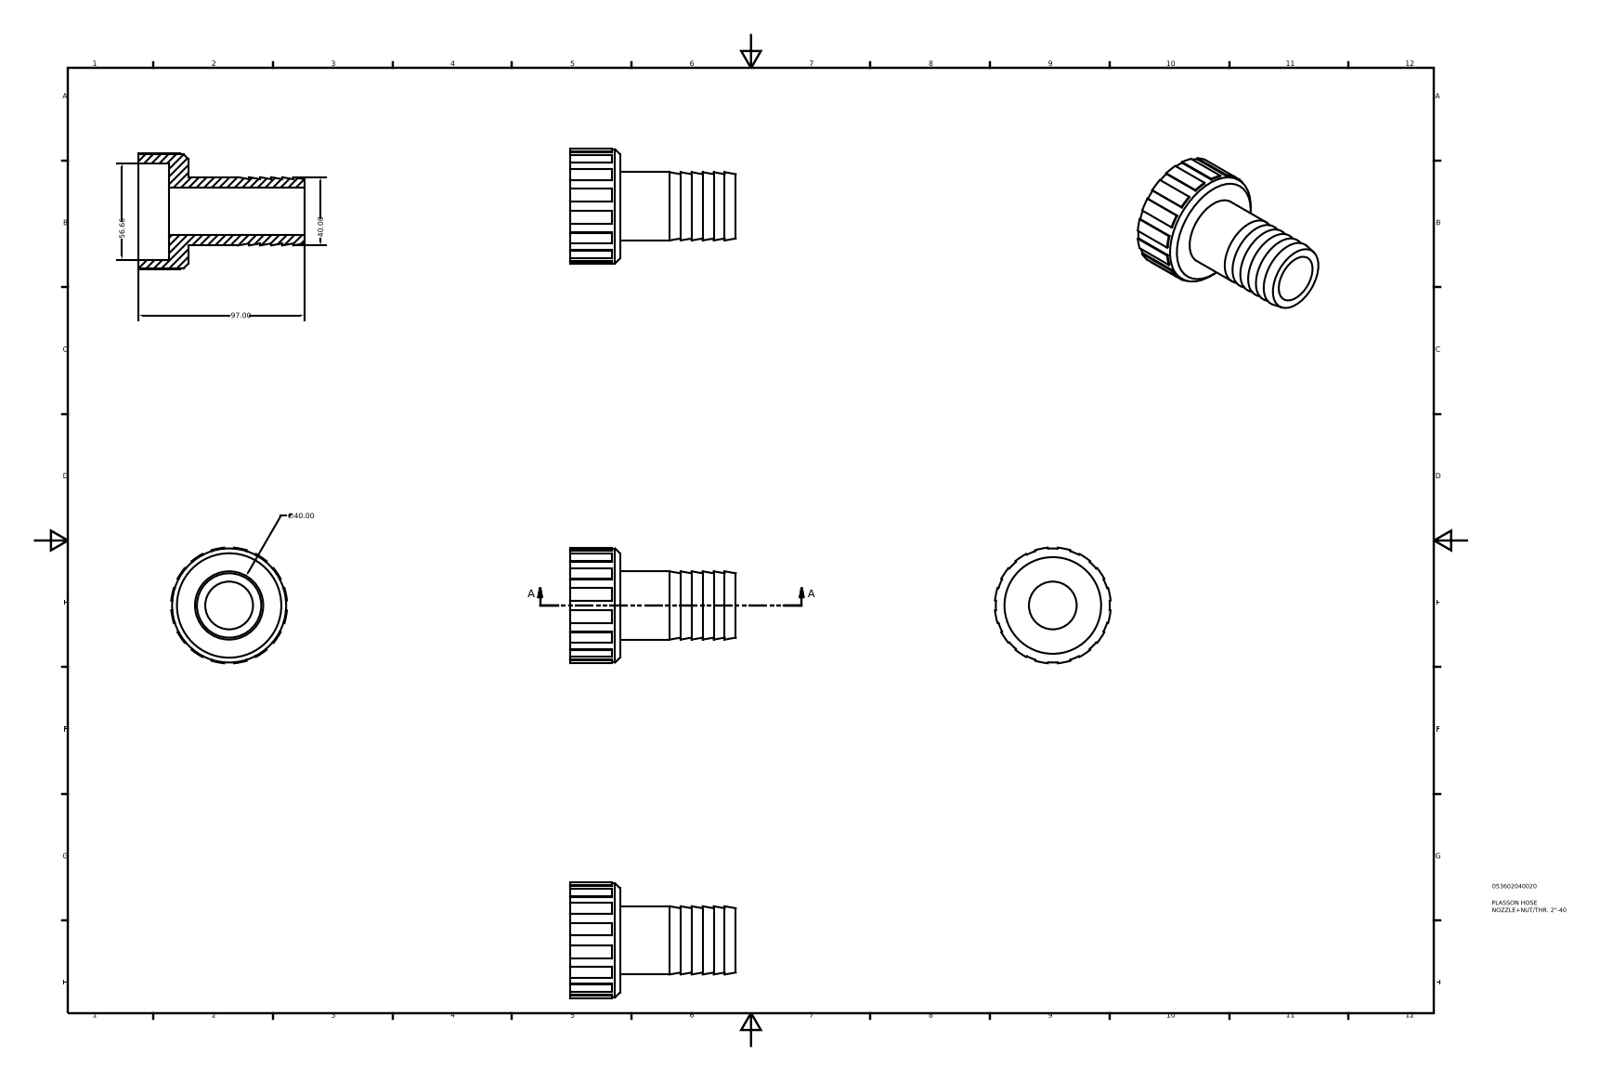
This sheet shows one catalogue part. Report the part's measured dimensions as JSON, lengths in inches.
{"part_name": "053602040020", "step_written_by": "Autodesk Inventor 2015 (AUTOMOTIVE_DESIGN)", "units": "inches", "bodies": {"solids": 1, "faces": 84, "planar": 57, "cylindrical": 20, "other": 7}, "overall_size": [3.819, 2.667, 2.667], "volume_in3": 5.651, "surface_area_in2": 48.51, "round_holes": [[1.102, 1], [2.231, 1]], "round_bosses_or_shafts": [[2.632, 1], [1.575, 1]], "partial_cylinders_radius": [[1.338, 1]], "face_to_face_distances": [0.458, 0.687, 1.146, 3.819, 3.131, 2.673, 0.509, 0.764, 0.255, 0.254]}
